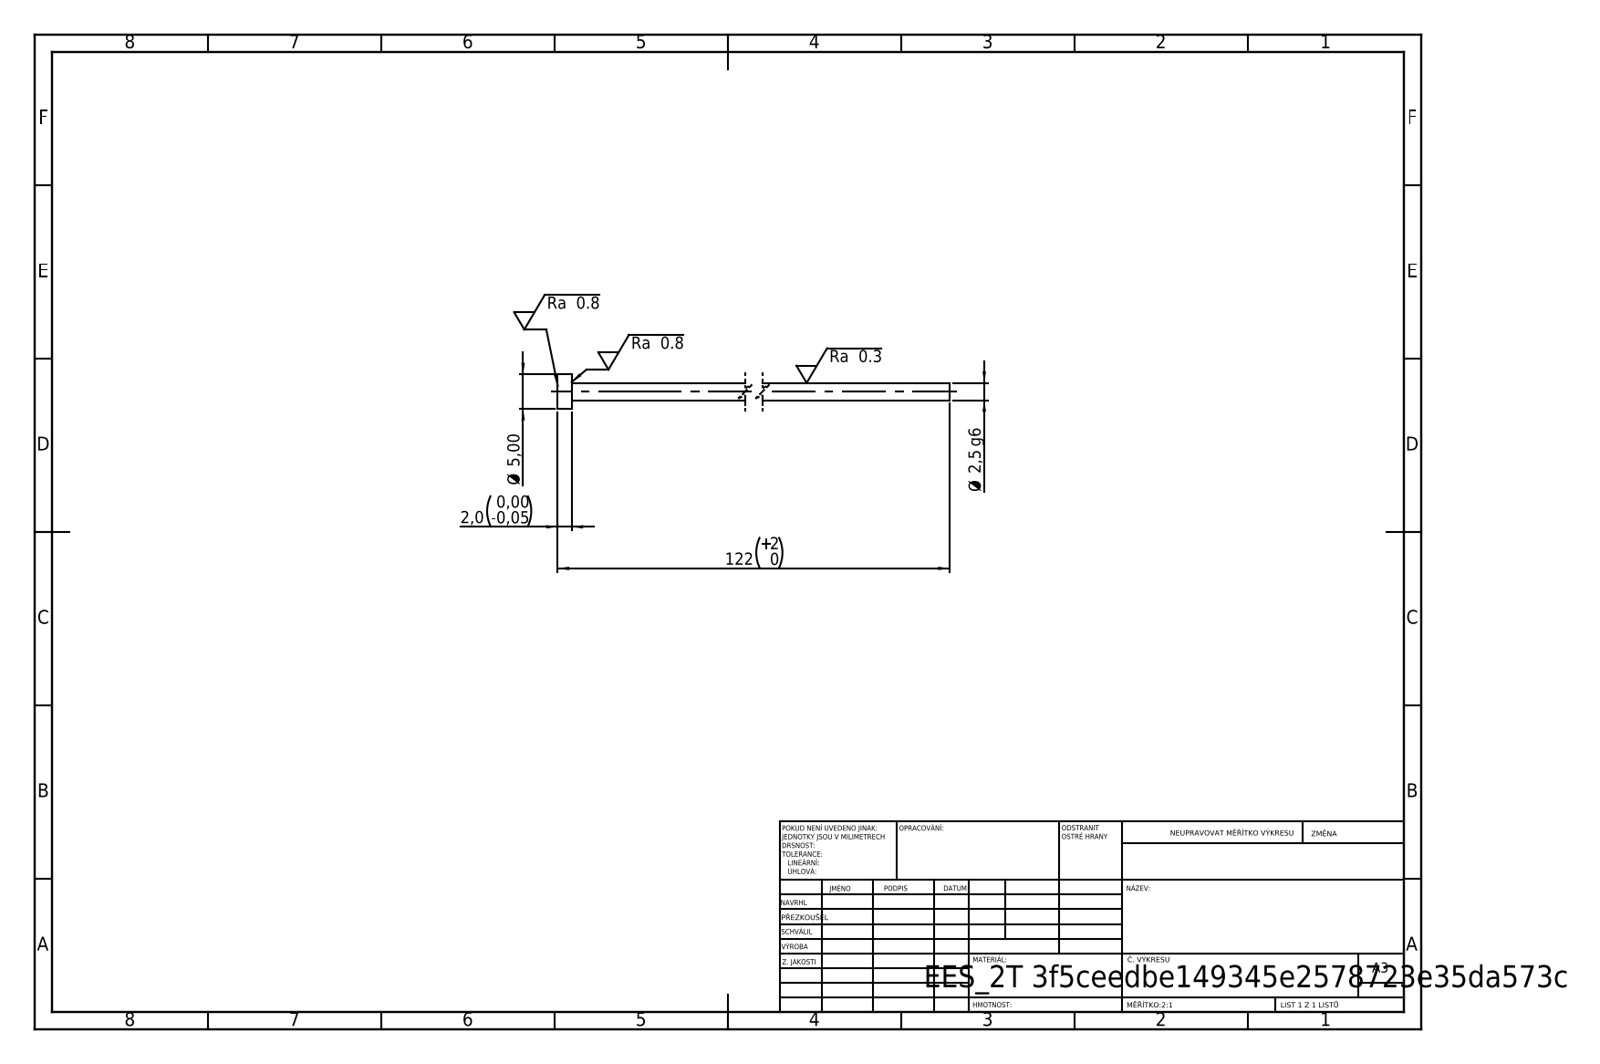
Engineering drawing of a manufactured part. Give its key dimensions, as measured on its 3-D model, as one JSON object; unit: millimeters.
{"step_written_by": "SolidWorks 2019 (CONFIG_CONTROL_DESIGN)", "units": "millimeters", "bodies": {"solids": 1, "faces": 7, "planar": 3, "cylindrical": 4, "other": 0}, "overall_size": [122, 5, 5], "volume_mm3": 628, "surface_area_mm2": 1013, "round_bosses_or_shafts": [[5, 1], [2.5, 1]], "face_to_face_distances": [2, 122, 120]}
